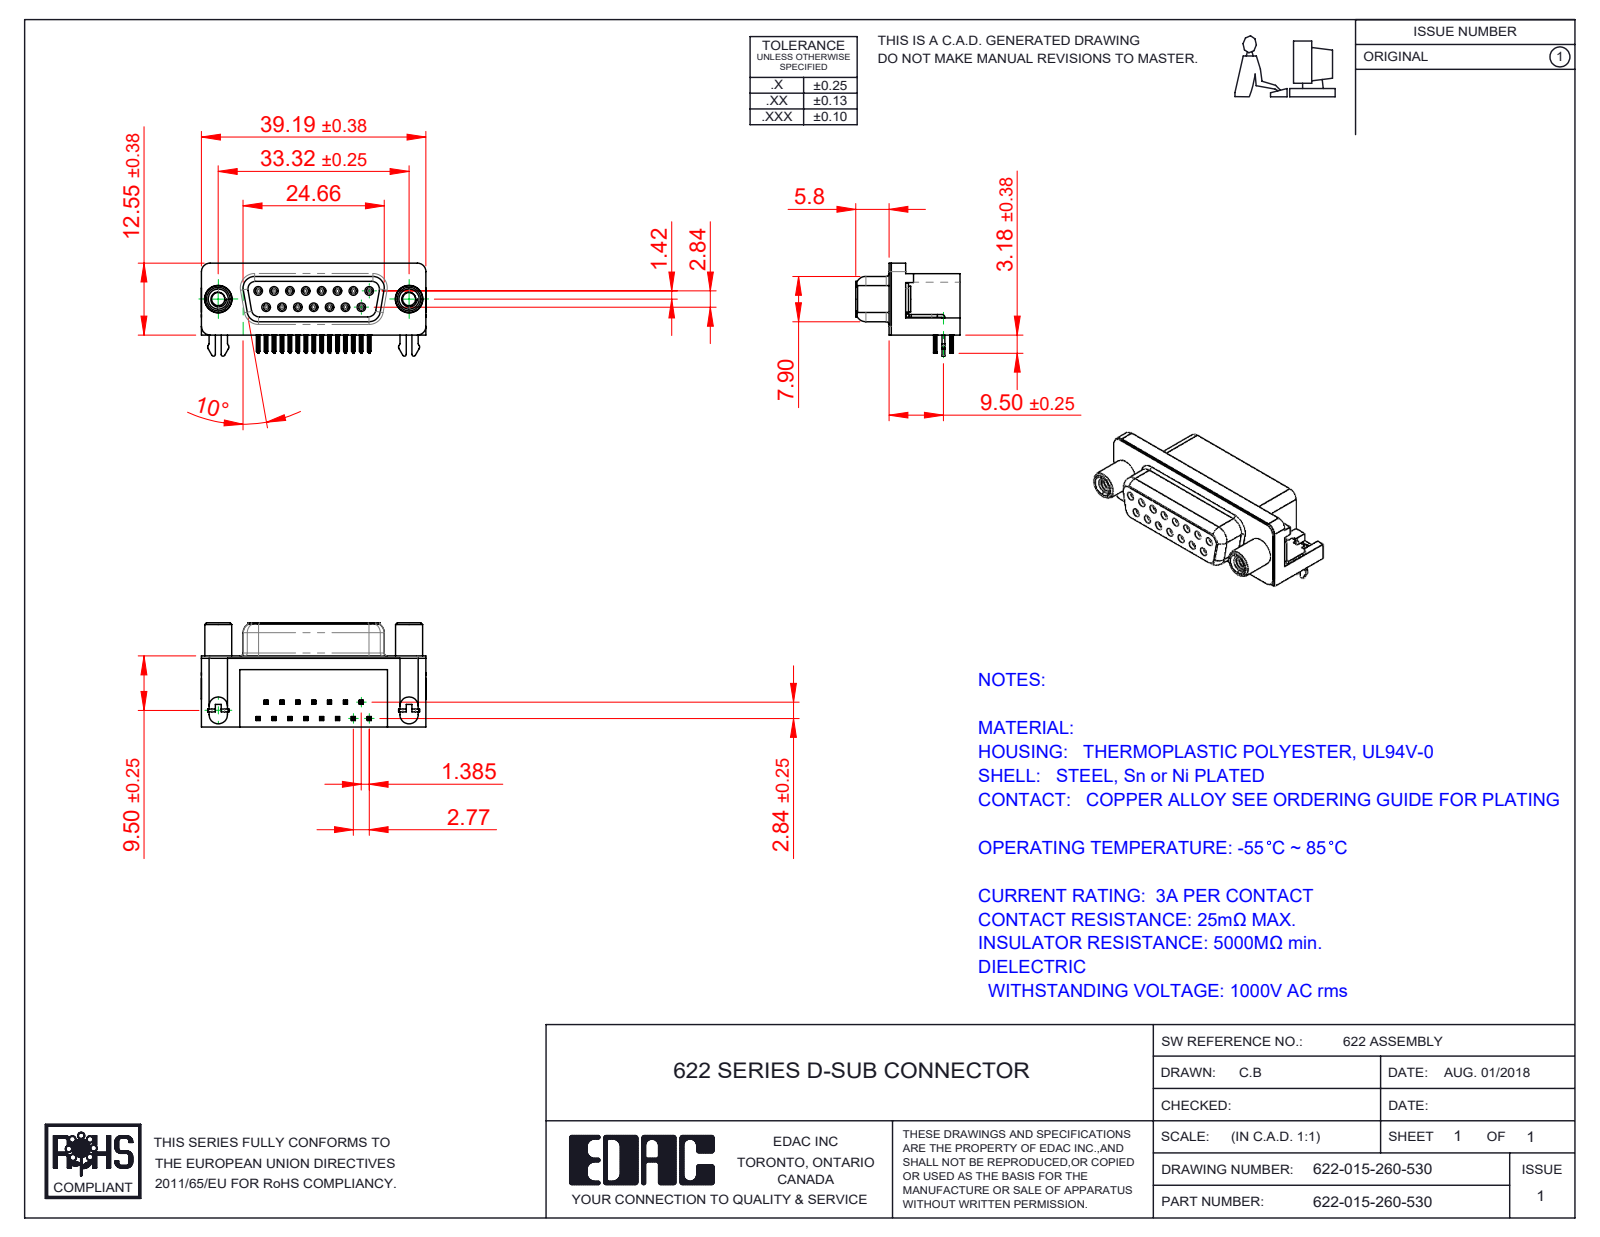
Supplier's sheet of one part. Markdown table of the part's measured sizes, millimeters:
| quantity | value |
| --- | --- |
| part name | 622-015-260-530; 622 2 Prong Board Lock; 622 Socket Bottom; 622 Round Threaded Standoff (+3 more) |
| STEP written by | SolidWorks 2016 (CONFIG_CONTROL_DESIGN) |
| units | millimeters |
| bodies | 21 solids, 2461 faces (1098 planar, 621 cylindrical, 742 other) |
| overall size | 39.22 × 18.2 × 16.25 |
| volume | 5 278 mm³ |
| surface area | 6 921 mm² |
| round holes (diameter × count) | 0.8 × 15, 0.9 × 15, 2.3 × 2, 3.1 × 2, 4 × 2, 4.8 × 2, 5 × 2 |
| round bosses / shafts (diameter × count) | 1.2 × 15, 4.9 × 2, 4.7 × 2, 4.5 × 2, 3.85 × 2 |
| partial cylindrical surfaces (radius × count) | 0.1 × 120, 0.15 × 60, 0.35 × 30, 1 × 18, 0.34 × 15, 0.5 × 10, 1.35 × 8, 1.5 × 8 |
| main face-to-face distances | 0.4, 12, 6.2, 10.35, 12.4, 2.9, 0.85, 6.65, 0.35, 5.8 |
| hole center spacings | 3.16, 2.77, 5.54, 8.31, 11.08, 5.03, 5.04, 7.48 |
